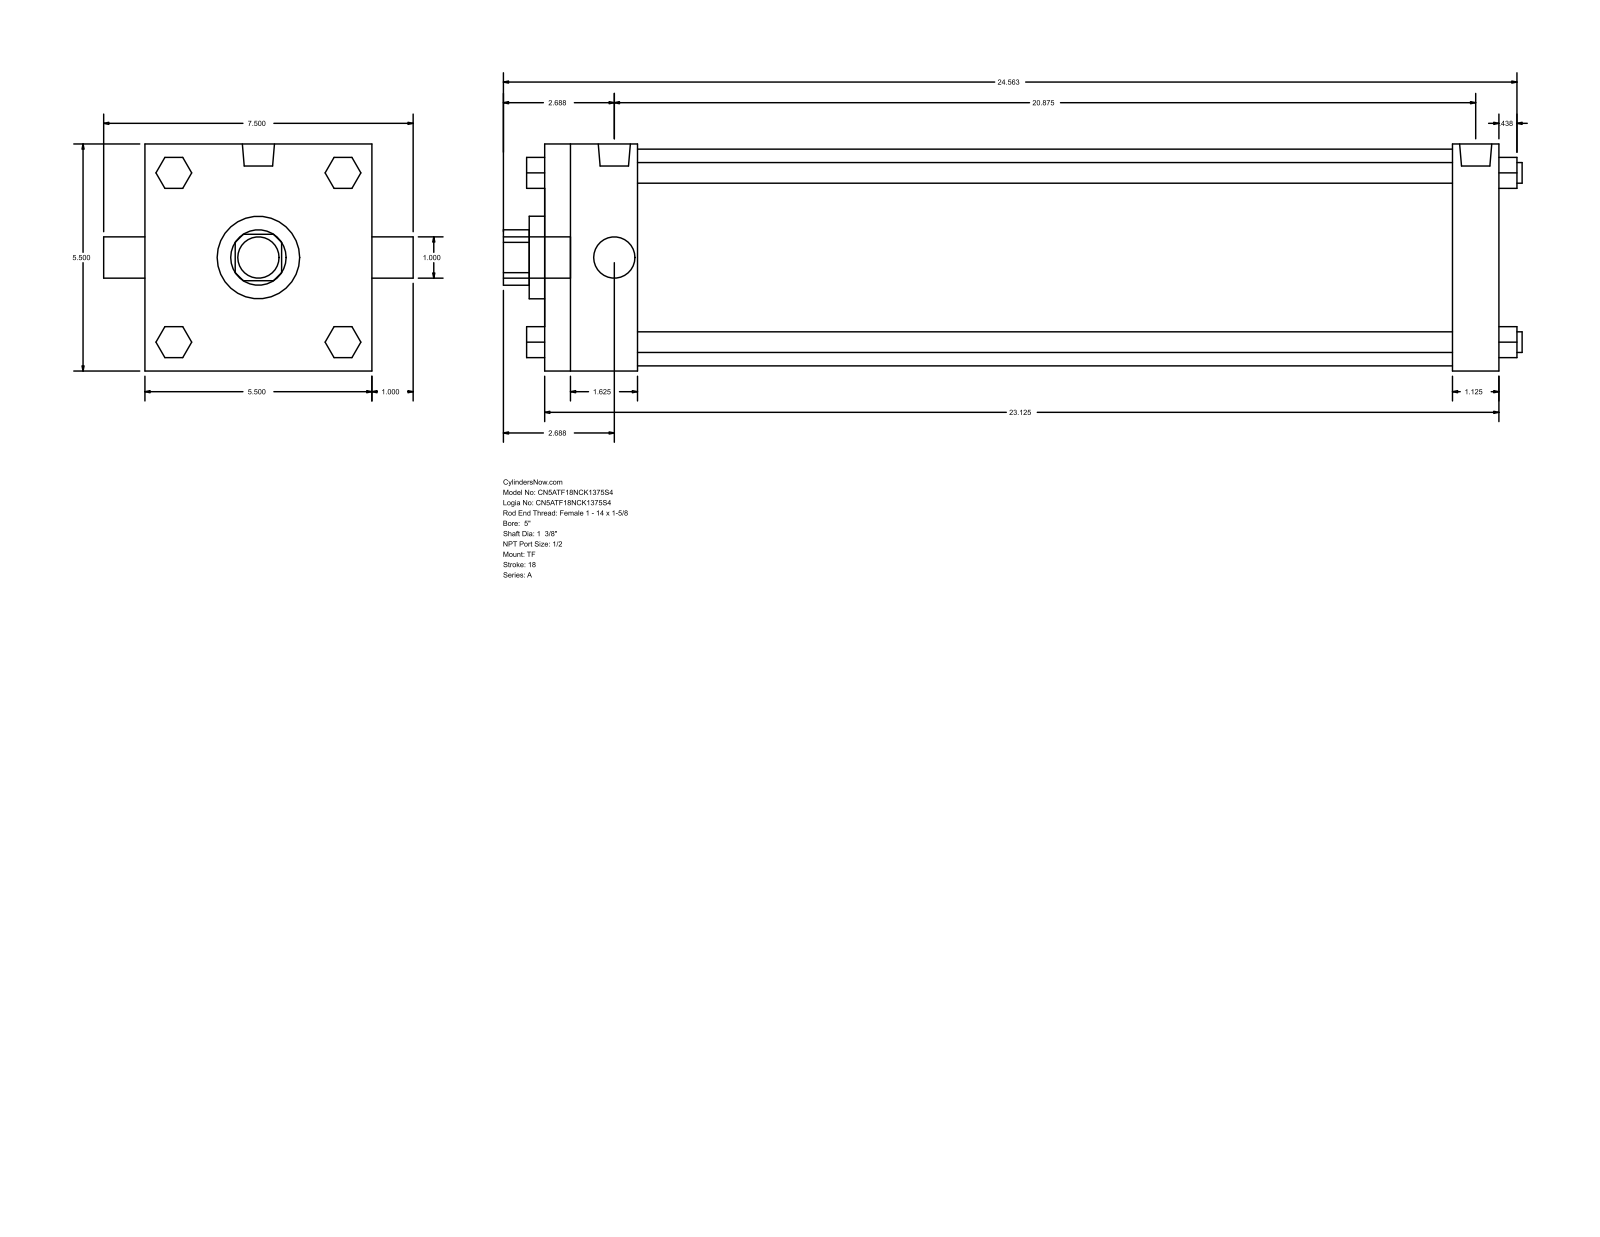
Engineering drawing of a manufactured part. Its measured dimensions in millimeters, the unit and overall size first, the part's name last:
Units: millimetres
Overall size (bounding box): 627.06 × 190.5 × 139.7
Round holes (diameter × count): ⌀25.4 ×1, ⌀34.92 ×1, ⌀50.8 ×1, ⌀133.35 ×1
Round bosses / shafts (diameter × count): ⌀12.7 ×4, ⌀8.73 ×3, ⌀19.77 ×2, ⌀25.4 ×1
Partial cylindrical surfaces — rounded edges, fillets, slot ends (radius × count): R17.06 ×1
Main face-to-face distances: 139.7, 587.37, 28.57, 558.8, 57.15, 501.65, 530.22, 19.05, 52.07, 90.18
Bodies: 0 solids, 120 faces (92 planar, 28 cylindrical, 0 other)
Part name (STEP PRODUCT): A_TF__0500_1.375
STEP written by: GSSL Pune (CONFIG_CONTROL_DESIGN)
